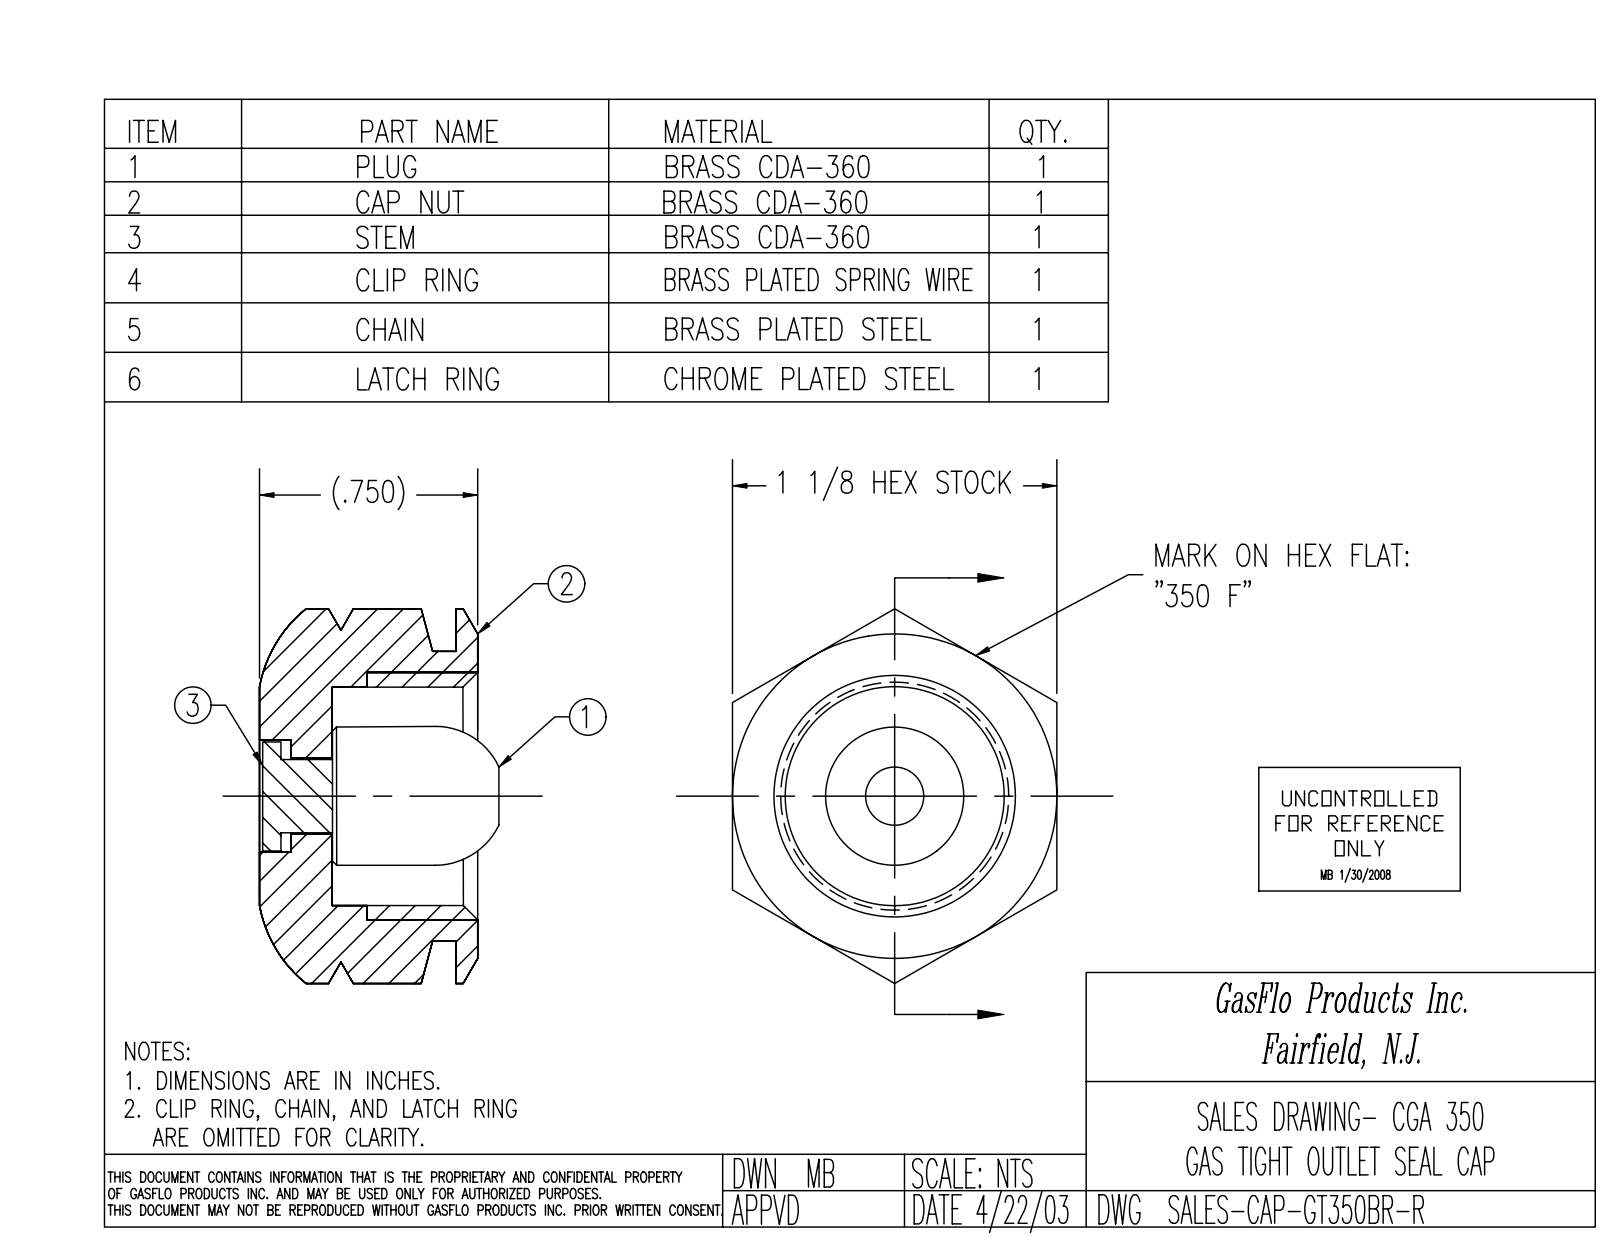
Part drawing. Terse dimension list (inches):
name: PRT-001151; PRT-000010; PRT-002245_RING-1.187D HALF; PRT-001141 (+6 more)
written by: SolidWorks 2018 (CONFIG_CONTROL_DESIGN)
unit: in
bodies: 14 solids, 462 faces (138 planar, 131 cylindrical, 193 other)
size: 5.521 × 2.304 × 1.125
volume: 0.7 in³; area: 13.64 in²
holes: 1× ⌀0.063, 1× ⌀0.12, 1× ⌀0.257, 1× ⌀0.382, 1× ⌀0.757
bosses: 30× ⌀0.063, 1× ⌀0.995, 1× ⌀0.475, 1× ⌀0.375, 1× ⌀0.25, 1× ⌀0.123, 1× ⌀0.1
rounds: 24× R0.005, 4× R0.25, 2× R0.01
face distances: 1.125, 0.25, 0.5, 0.75, 0.073, 0.677, 0.427, 1.125, 0.046, 0.296
